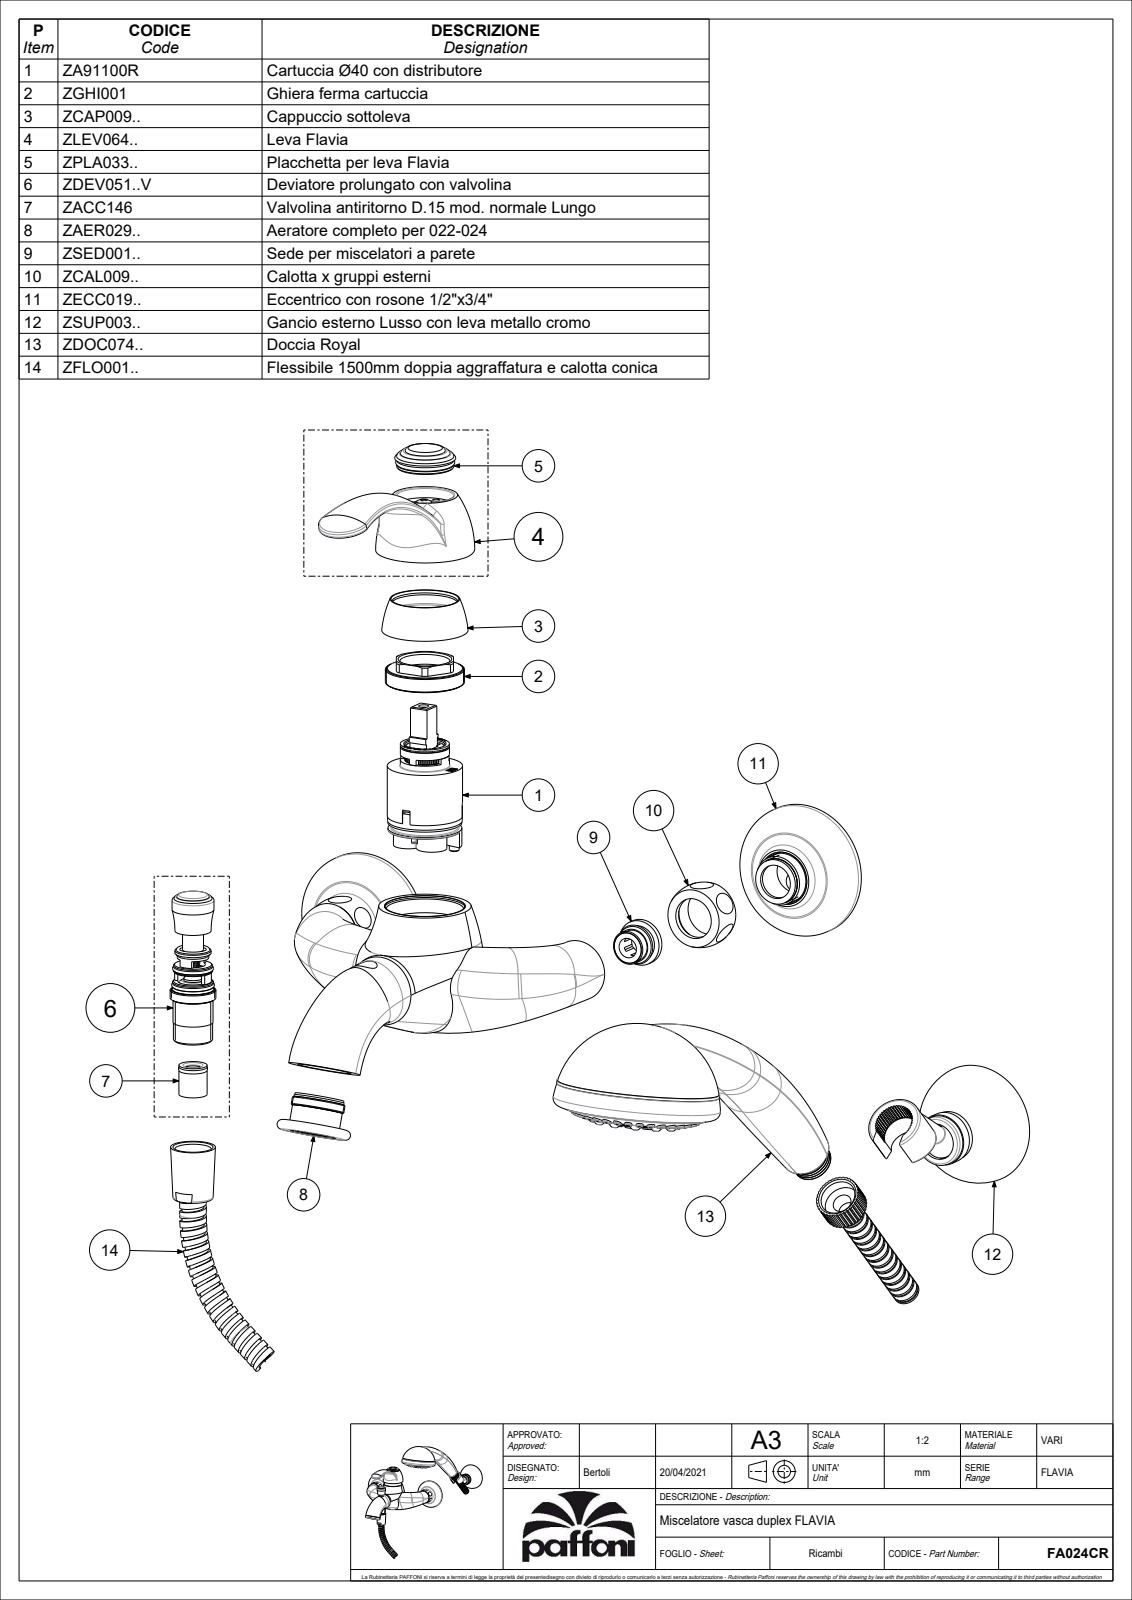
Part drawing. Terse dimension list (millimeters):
name: 3021164TO; 2081067GR; 4061052CR; 2041539GR (+8 more)
written by: CREO PARAMETRIC BY PTC INC, 2020044 (CONFIG_CONTROL_DESIGN)
unit: mm
bodies: 32 solids, 4927 faces (2058 planar, 1385 cylindrical, 1484 other)
size: 354.06 × 309.06 × 238.05
volume: 633 077 mm³; area: 303 127 mm²
holes: 91× ⌀0.5, 40× ⌀1.5, 16× ⌀2.5, 12× ⌀1.2, 12× ⌀3.9, 12× ⌀7.4, 5× ⌀18, 4× ⌀19, 3× ⌀7.2, 3× ⌀10, 3× ⌀14, 2× ⌀4
bosses: 12× ⌀4.4, 12× ⌀2, 7× ⌀13, 5× ⌀24, 4× ⌀16.5, 3× ⌀27, 3× ⌀20.5, 3× ⌀16
rounds: 38× R0.5, 33× R0.3, 20× R1.5, 12× R1, 12× R3.5, 8× R1.6, 8× R2.2, 5× R38.68
face distances: 3, 1.5, 2.5, 1, 9, 6.5, 7, 5, 6.8, 13.4
hole spacings: 21.8, 15, 3.82, 7.64, 10.7, 2, 5.73, 30.83
